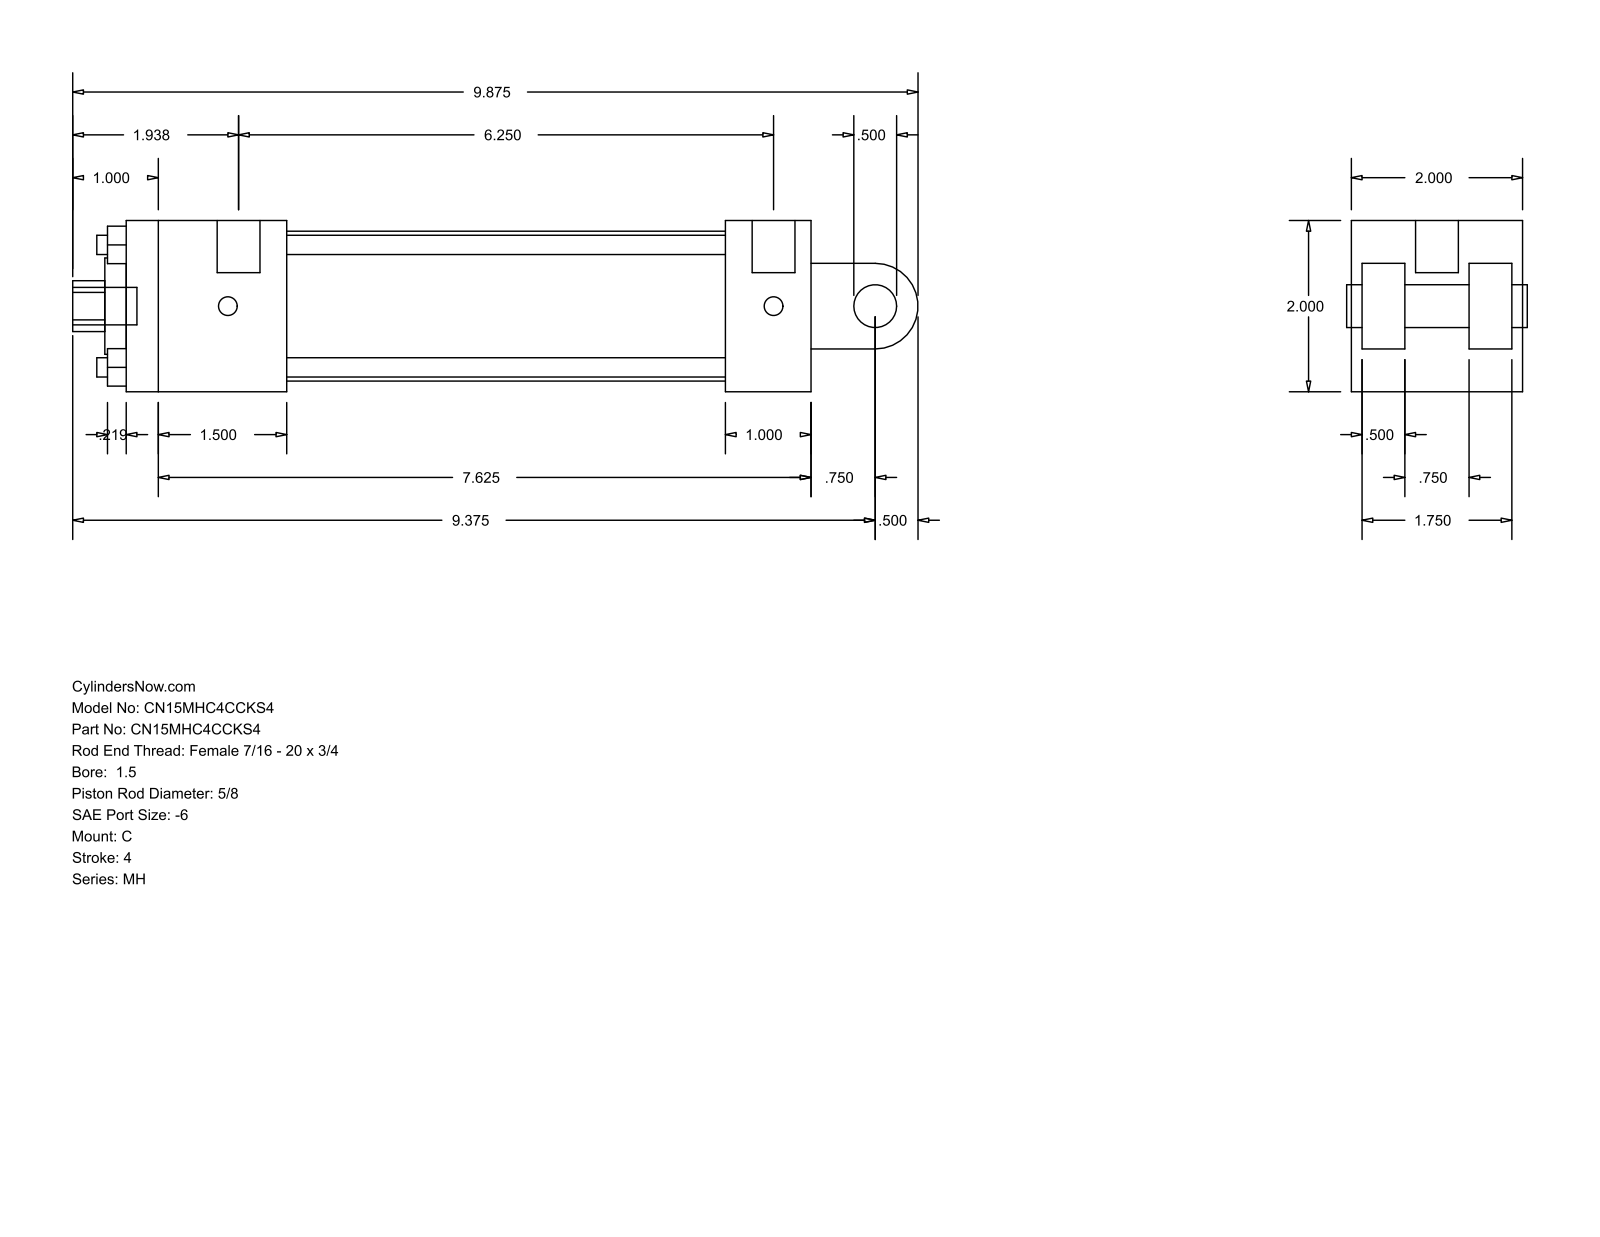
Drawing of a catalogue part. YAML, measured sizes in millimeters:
part_name: "MH_C__0150_0.625"
step_written_by: "GSSL Pune (CONFIG_CONTROL_DESIGN)"
units: millimeters
bodies: {solids: 0, faces: 99, planar: 70, cylindrical: 29, other: 0}
overall_size: [250.82, 50.8, 50.8]
round_holes:
  - {diameter: 5.71, count: 4}
  - {diameter: 5.56, count: 2}
  - {diameter: 12.7, count: 1}
  - {diameter: 15.88, count: 1}
  - {diameter: 28.57, count: 1}
  - {diameter: 44.45, count: 1}
round_bosses_or_shafts:
  - {diameter: 12.7, count: 2}
  - {diameter: 5.56, count: 2}
  - {diameter: 11.11, count: 1}
partial_cylinders:
  - {radius: 7.54, count: 1}
  - {radius: 12.7, count: 1}
face_to_face_distances: [50.8, 12.7, 203.19, 3.17, 47.63, 15.87, 34.93, 31.76, 38.1, 47.62]
hole_center_spacings: [25.68, 36.32, 51.36]
